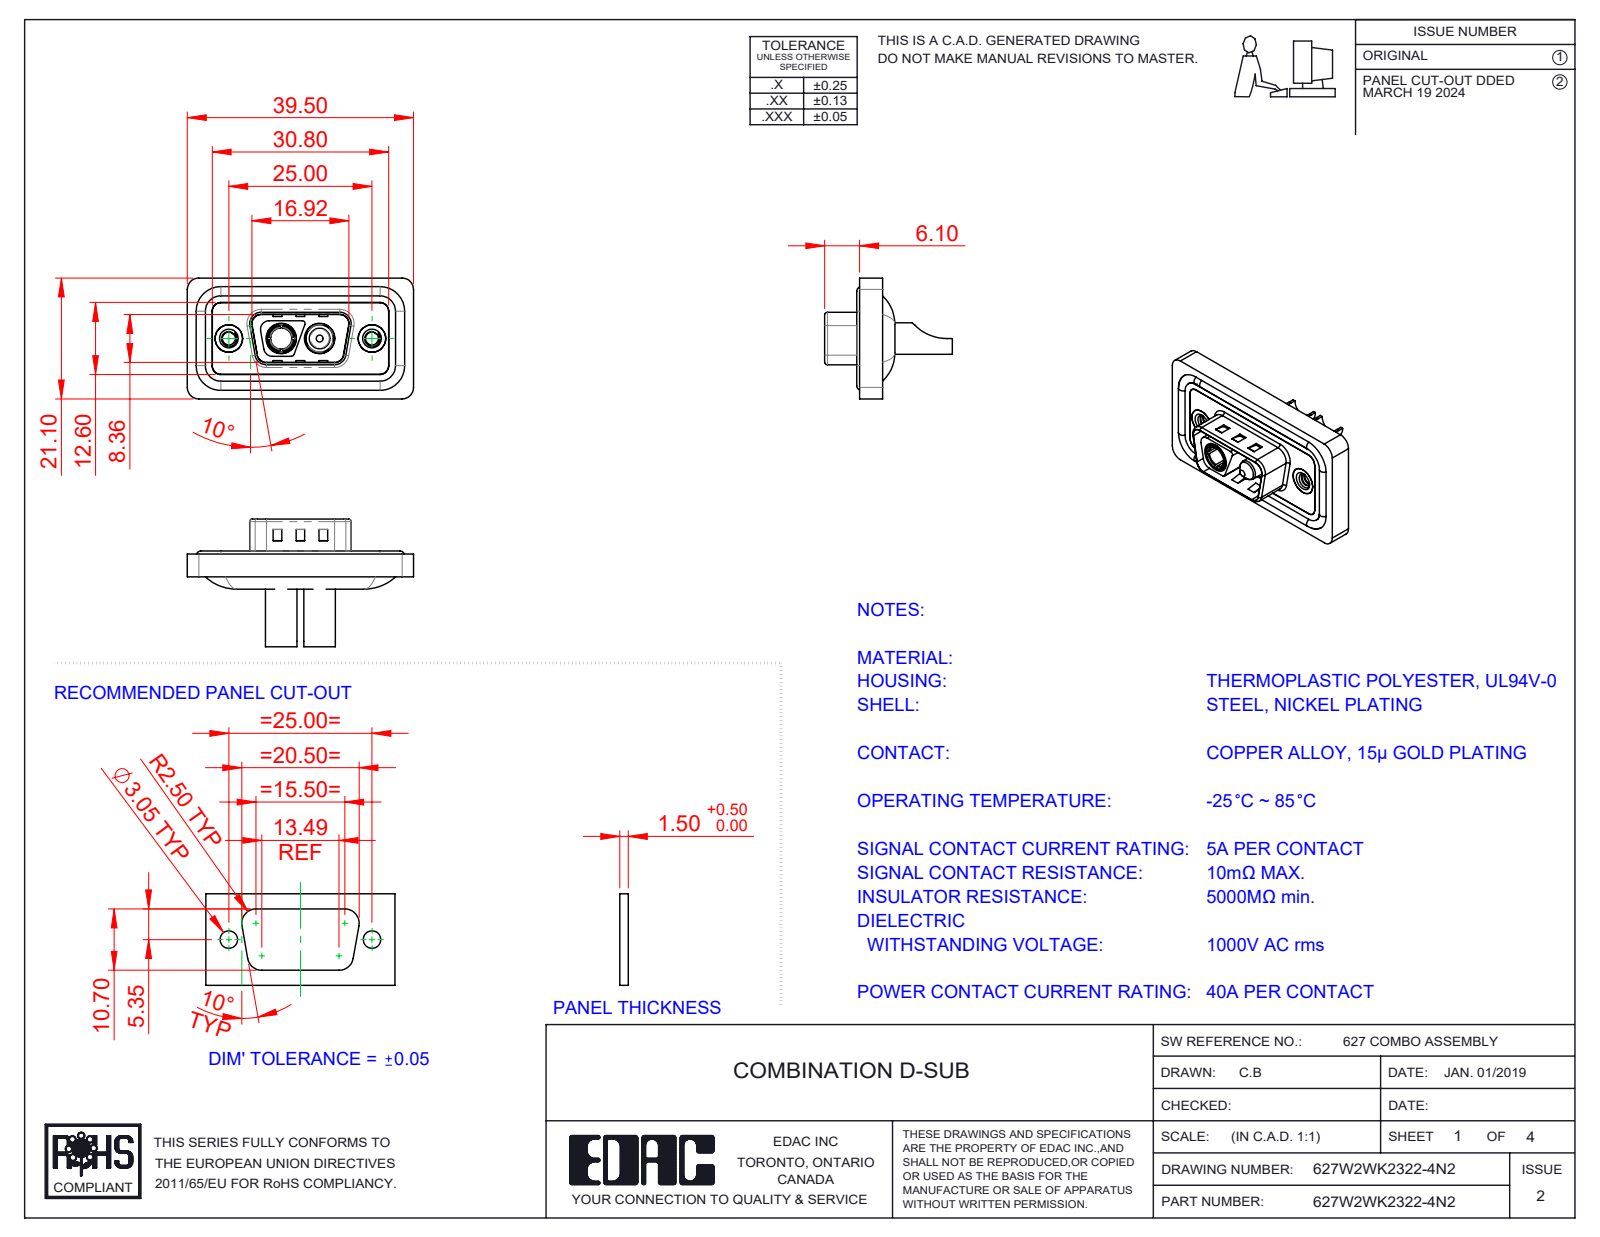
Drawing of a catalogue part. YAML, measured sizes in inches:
part_name: "627Combo Waterproof Housing_09 Contacts; 627Combo Housing_2WK2; Power Socket_40A SC; 627Combo Threaded Rivet_2 (+4 more)"
step_written_by: "SolidWorks 2023 (CONFIG_CONTROL_DESIGN)"
units: inches
bodies: {solids: 11, faces: 542, planar: 193, cylindrical: 229, other: 120}
overall_size: [1.555, 0.878, 0.831]
volume: 0.283
surface_area: 11.81
round_holes:
  - {diameter: 0.089, count: 2}
  - {diameter: 0.157, count: 2}
  - {diameter: 0.181, count: 2}
  - {diameter: 0.189, count: 2}
  - {diameter: 0.191, count: 2}
  - {diameter: 0.197, count: 2}
  - {diameter: 0.209, count: 2}
  - {diameter: 0.146, count: 1}
round_bosses_or_shafts:
  - {diameter: 0.063, count: 4}
  - {diameter: 0.217, count: 2}
  - {diameter: 0.205, count: 2}
  - {diameter: 0.193, count: 2}
  - {diameter: 0.187, count: 2}
  - {diameter: 0.148, count: 2}
  - {diameter: 0.195, count: 1}
  - {diameter: 0.142, count: 1}
partial_cylinders:
  - {radius: 0.059, count: 24}
  - {radius: 0.079, count: 18}
  - {radius: 0.02, count: 10}
  - {radius: 0.063, count: 8}
  - {radius: 0.01, count: 4}
  - {radius: 0.024, count: 4}
  - {radius: 0.026, count: 4}
  - {radius: 0.035, count: 4}
face_to_face_distances: [0.016, 0.043, 0.114, 0.02, 0.122, 0.063, 0.098, 0.071, 0.126, 0.059]
hole_center_spacings: [0.36, 0.624, 0.265, 0.984]
